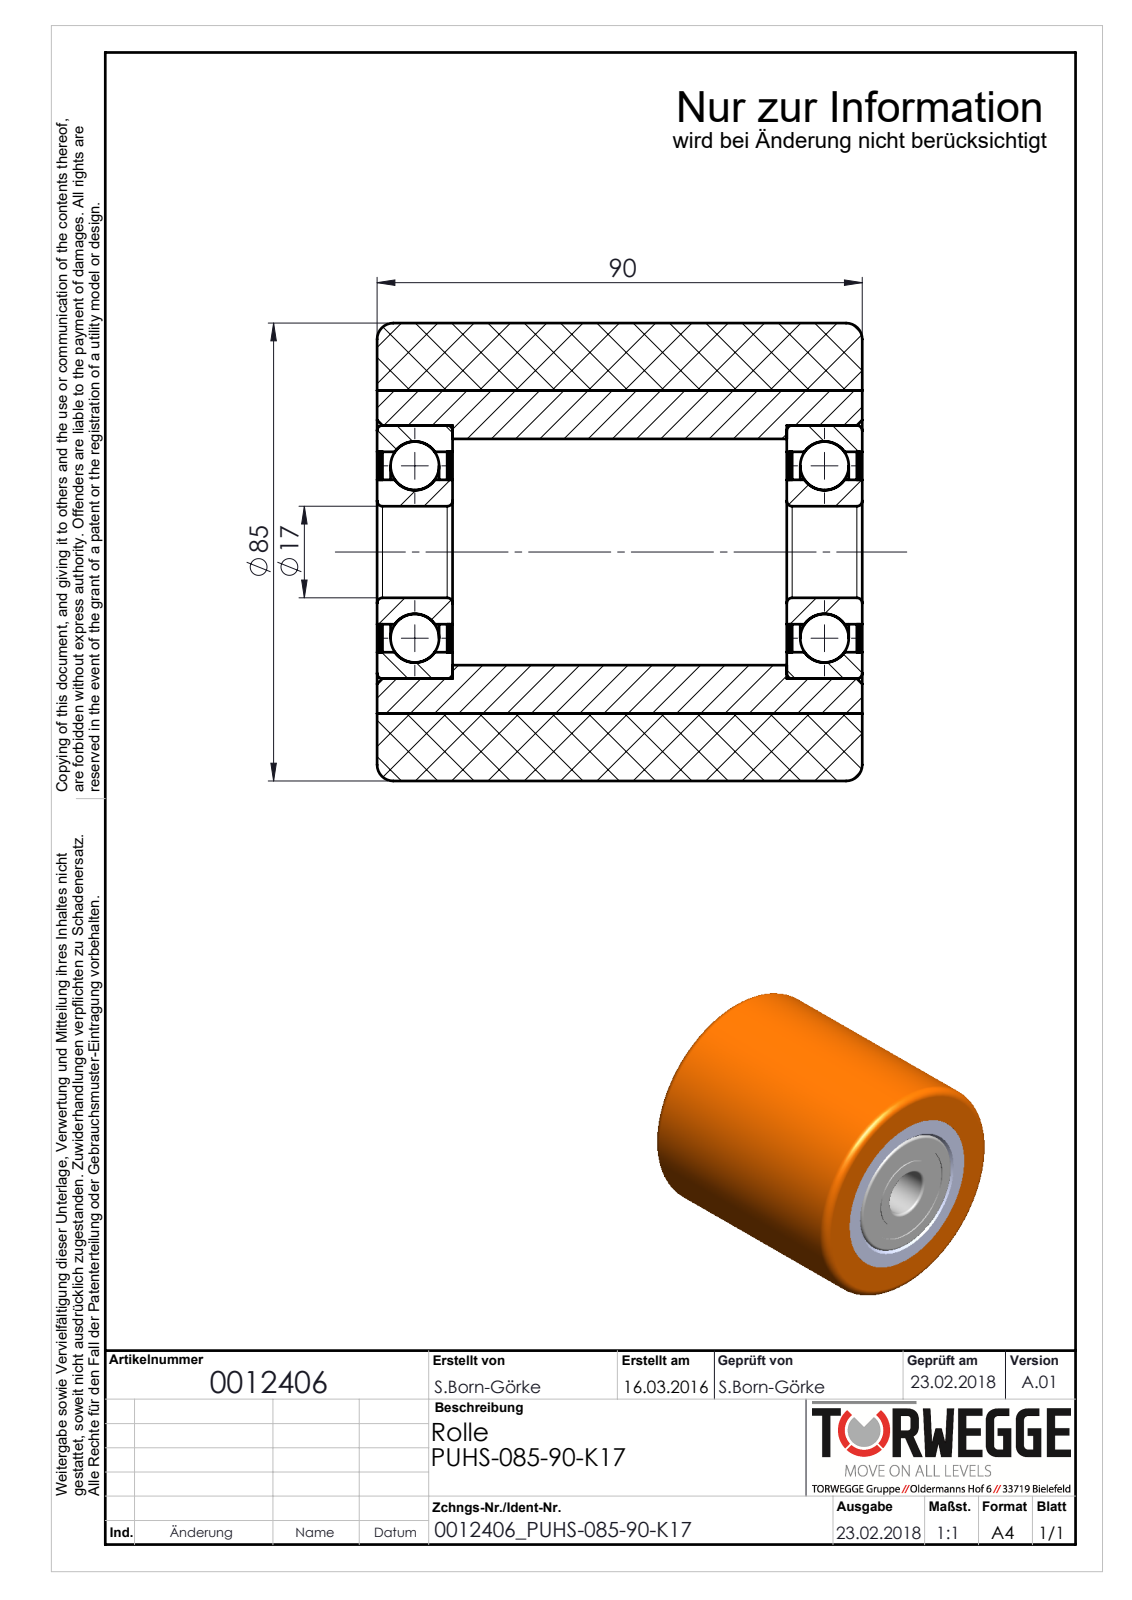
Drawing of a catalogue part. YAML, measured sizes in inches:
part_name: "0012406_PUHS-085-90-K17"
step_written_by: "SolidWorks 2016 (CONFIG_CONTROL_DESIGN)"
units: inches
bodies: {solids: 12, faces: 118, planar: 22, cylindrical: 52, other: 44}
overall_size: [3.543, 3.346, 3.346]
volume: 25.14
surface_area: 160.7
round_holes:
  - {diameter: 0.669, count: 1}
  - {diameter: 1.055, count: 1}
  - {diameter: 1.465, count: 1}
  - {diameter: 1.654, count: 1}
  - {diameter: 1.85, count: 1}
  - {diameter: 2.362, count: 1}
round_bosses_or_shafts:
  - {diameter: 3.346, count: 1}
face_to_face_distances: [2.992, 0.02, 3.543, 0.512, 0.551, 0.039, 0.531, 3.012, 0.492, 2.972]
